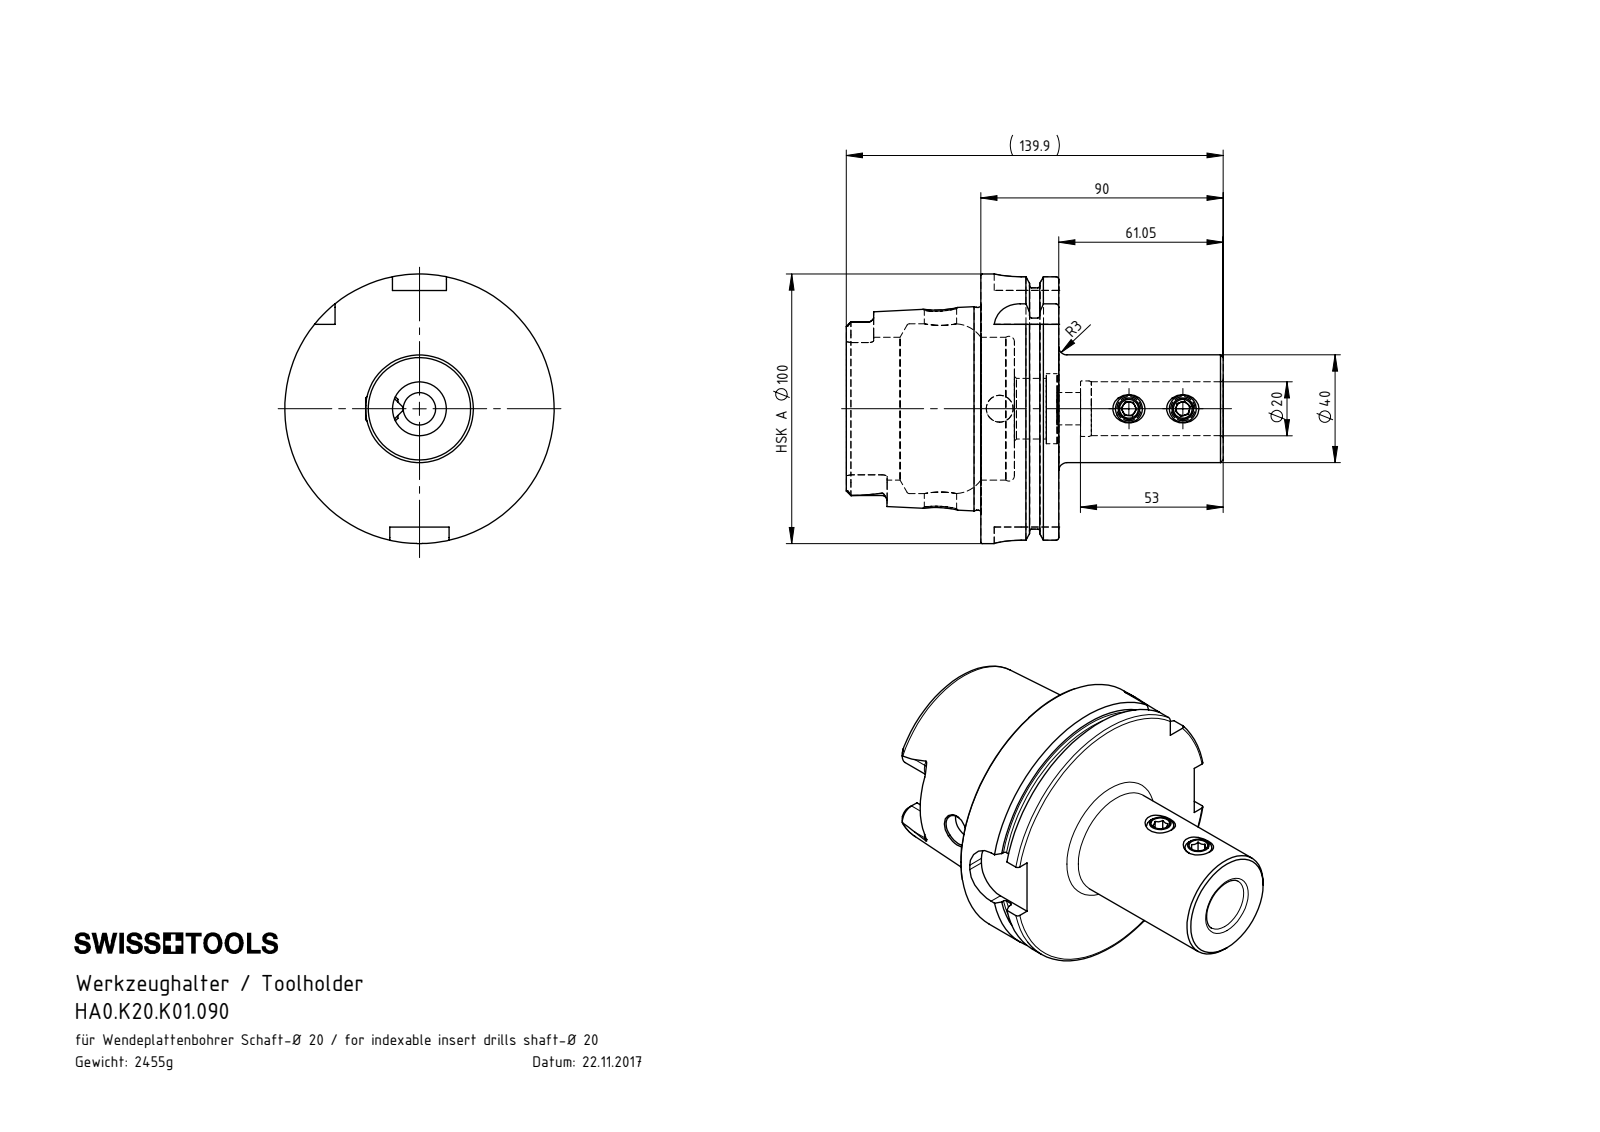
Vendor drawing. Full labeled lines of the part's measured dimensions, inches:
Part name (STEP PRODUCT): HA0-K20.K01.090_A_Fertigbearbeitung; K20-ER1.010.012_PreviewCfg; HA0.K20.K01.090; K20-ER2.010.014_PreviewCfg
STEP written by: SolidWorks 2017 (AUTOMOTIVE_DESIGN)
Units: inches
Bodies: 3 solids, 167 faces (69 planar, 40 cylindrical, 58 other)
Overall size (bounding box): 5.508 × 3.937 × 3.937
Volume: 19.07 in³ · Surface area: 96.09 in²
Round holes (diameter × count): ⌀0.197 ×2, ⌀0.354 ×2, ⌀0.472 ×2, ⌀0.394 ×1, ⌀0.787 ×1, ⌀0.811 ×1, ⌀0.886 ×1, ⌀1.024 ×1, ⌀2.087 ×1, ⌀2.48 ×1
Round bosses / shafts (diameter × count): ⌀0.394 ×2, ⌀3.937 ×1, ⌀3.62 ×1, ⌀2.963 ×1, ⌀1.575 ×1
Partial cylindrical surfaces — rounded edges, fillets, slot ends (radius × count): R0.075 ×6, R0.394 ×4, R0.19 ×2, R0.192 ×2
Main face-to-face distances: 1.14, 0.49, 0.65, 1.965, 2.455, 3.104, 5.508, 3.543, 3.053, 2.404
Hole centre spacings: 0.787, 1.89, 2.677
